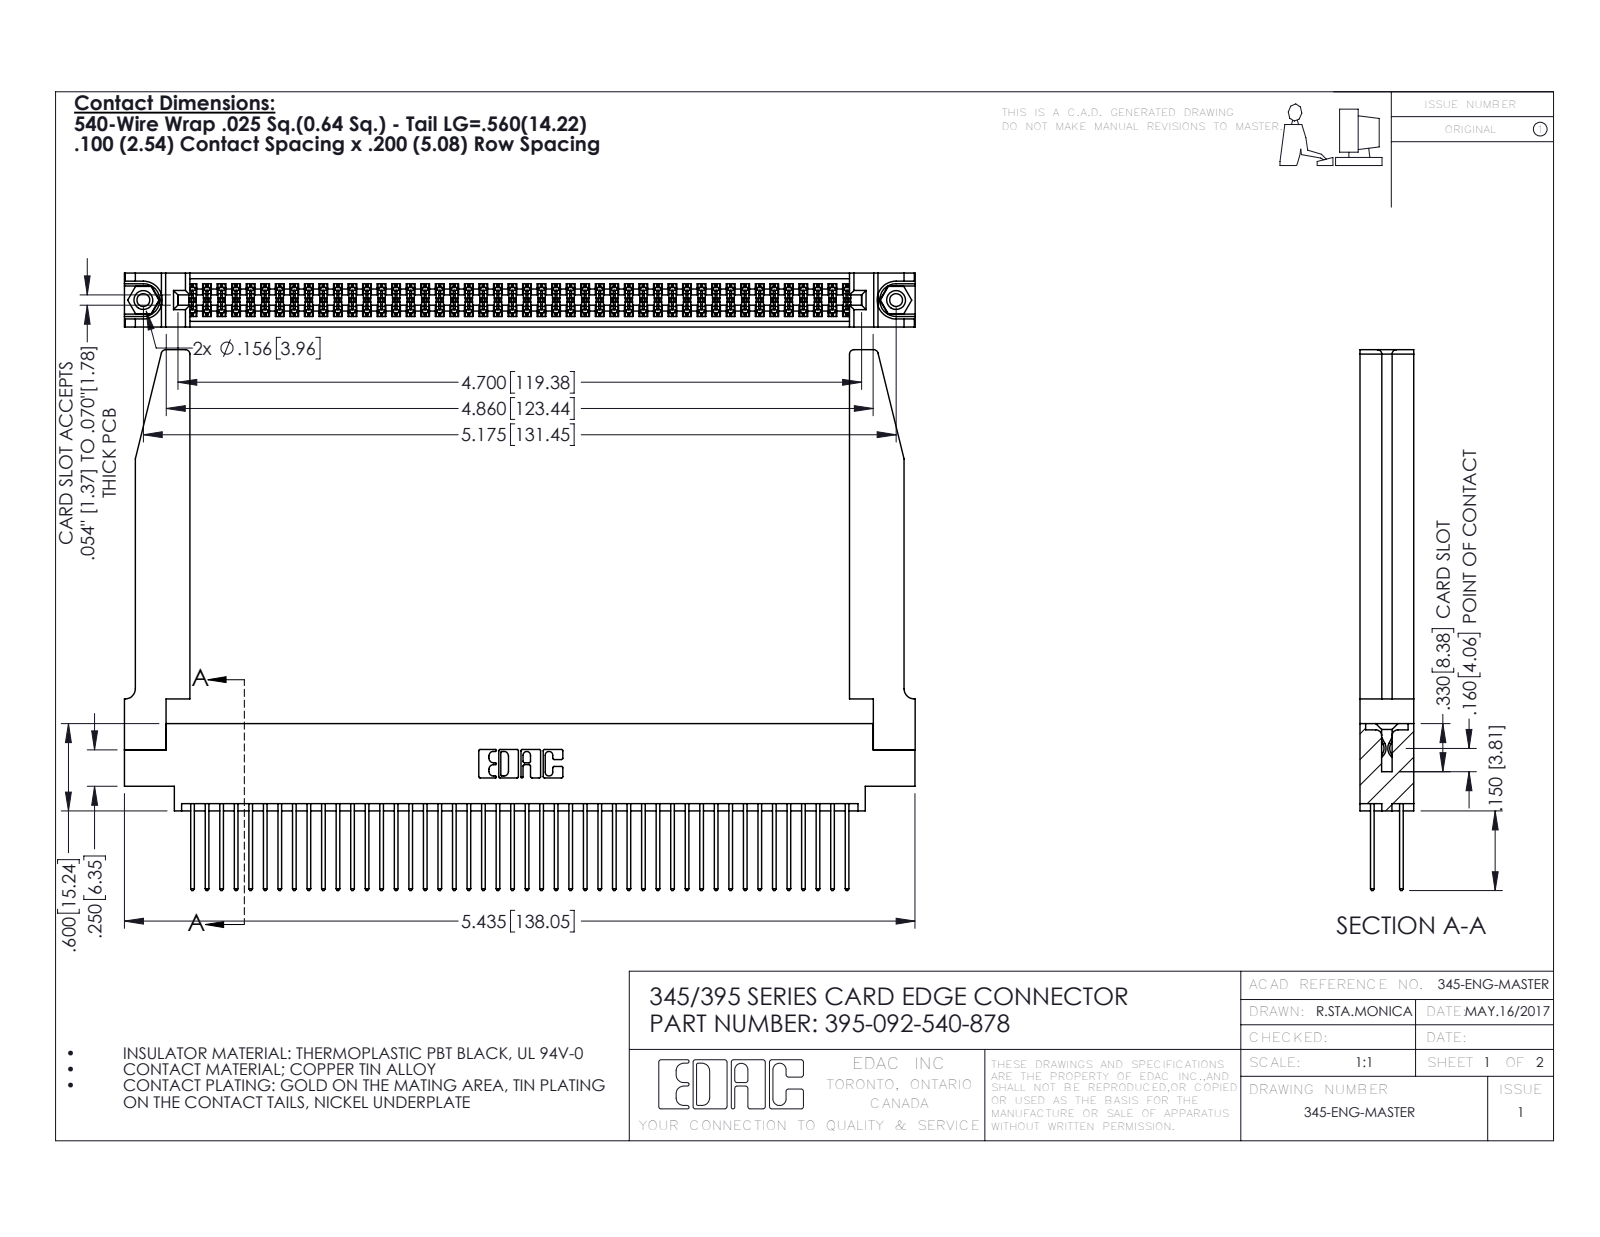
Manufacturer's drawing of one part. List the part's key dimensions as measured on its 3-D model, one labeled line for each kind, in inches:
Part name (STEP PRODUCT): 345-250-001_345-250-001-102; 345-292-001_345-293-140; 345-220-078_345-220-078; 345 Part_0.170 Offset - 0.156 Dia-TH (+1 more)
STEP written by: SolidWorks 2016 (CONFIG_CONTROL_DESIGN)
Units: inches
Bodies: 97 solids, 4964 faces (3262 planar, 1650 cylindrical, 52 other)
Overall size (bounding box): 5.436 × 3.717 × 0.37
Volume: 1.309 in³ · Surface area: 44.81 in²
Round holes (diameter × count): ⌀0.089 ×2, ⌀0.125 ×2, ⌀0.156 ×2, ⌀0.064 ×1
Round bosses / shafts (diameter × count): ⌀0.155 ×2
Partial cylindrical surfaces — rounded edges, fillets, slot ends (radius × count): R0.006 ×138, R0.01 ×92, R0.01 ×22, R0.03 ×8, R0.007 ×6, R0.031 ×6, R0.026 ×3, R0.014 ×2
Main face-to-face distances: 0.072, 0.298, 0.37, 0.2, 0.098, 0.272, 0.025, 0.225, 0.175, 0.148
Hole centre spacings: 0.27, 4.939, 5.175
